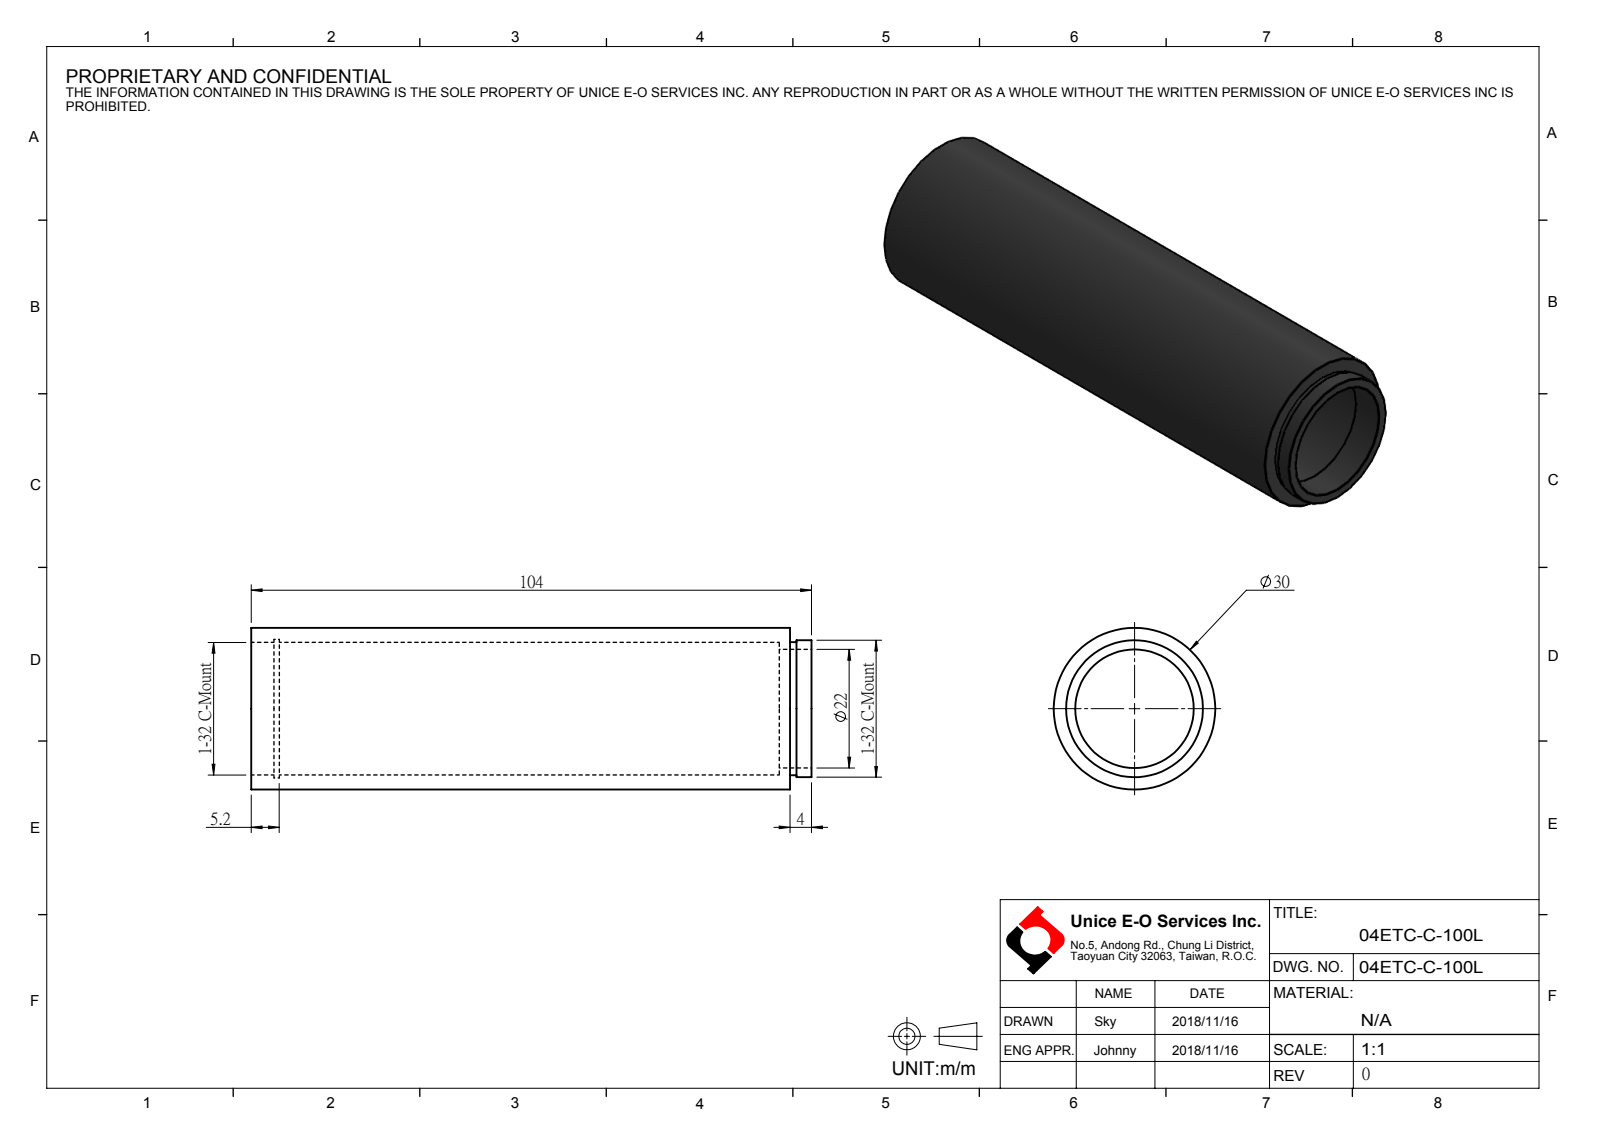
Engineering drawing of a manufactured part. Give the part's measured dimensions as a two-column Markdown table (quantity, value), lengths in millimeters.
| quantity | value |
| --- | --- |
| part name | 04ETC-C-100L |
| STEP written by | SolidWorks 2016 (AUTOMOTIVE_DESIGN) |
| units | millimeters |
| bodies | 0 solids, 18 faces (4 planar, 14 cylindrical, 0 other) |
| overall size | 104 × 30 × 30 |
| round holes (diameter × count) | 22 × 1, 24.6 × 1, 25.7 × 1 |
| round bosses / shafts (diameter × count) | 30 × 1, 25.4 × 1, 24.7 × 1 |
| main face-to-face distances | 100, 104, 4, 5.2, 94.8, 98.8 |
